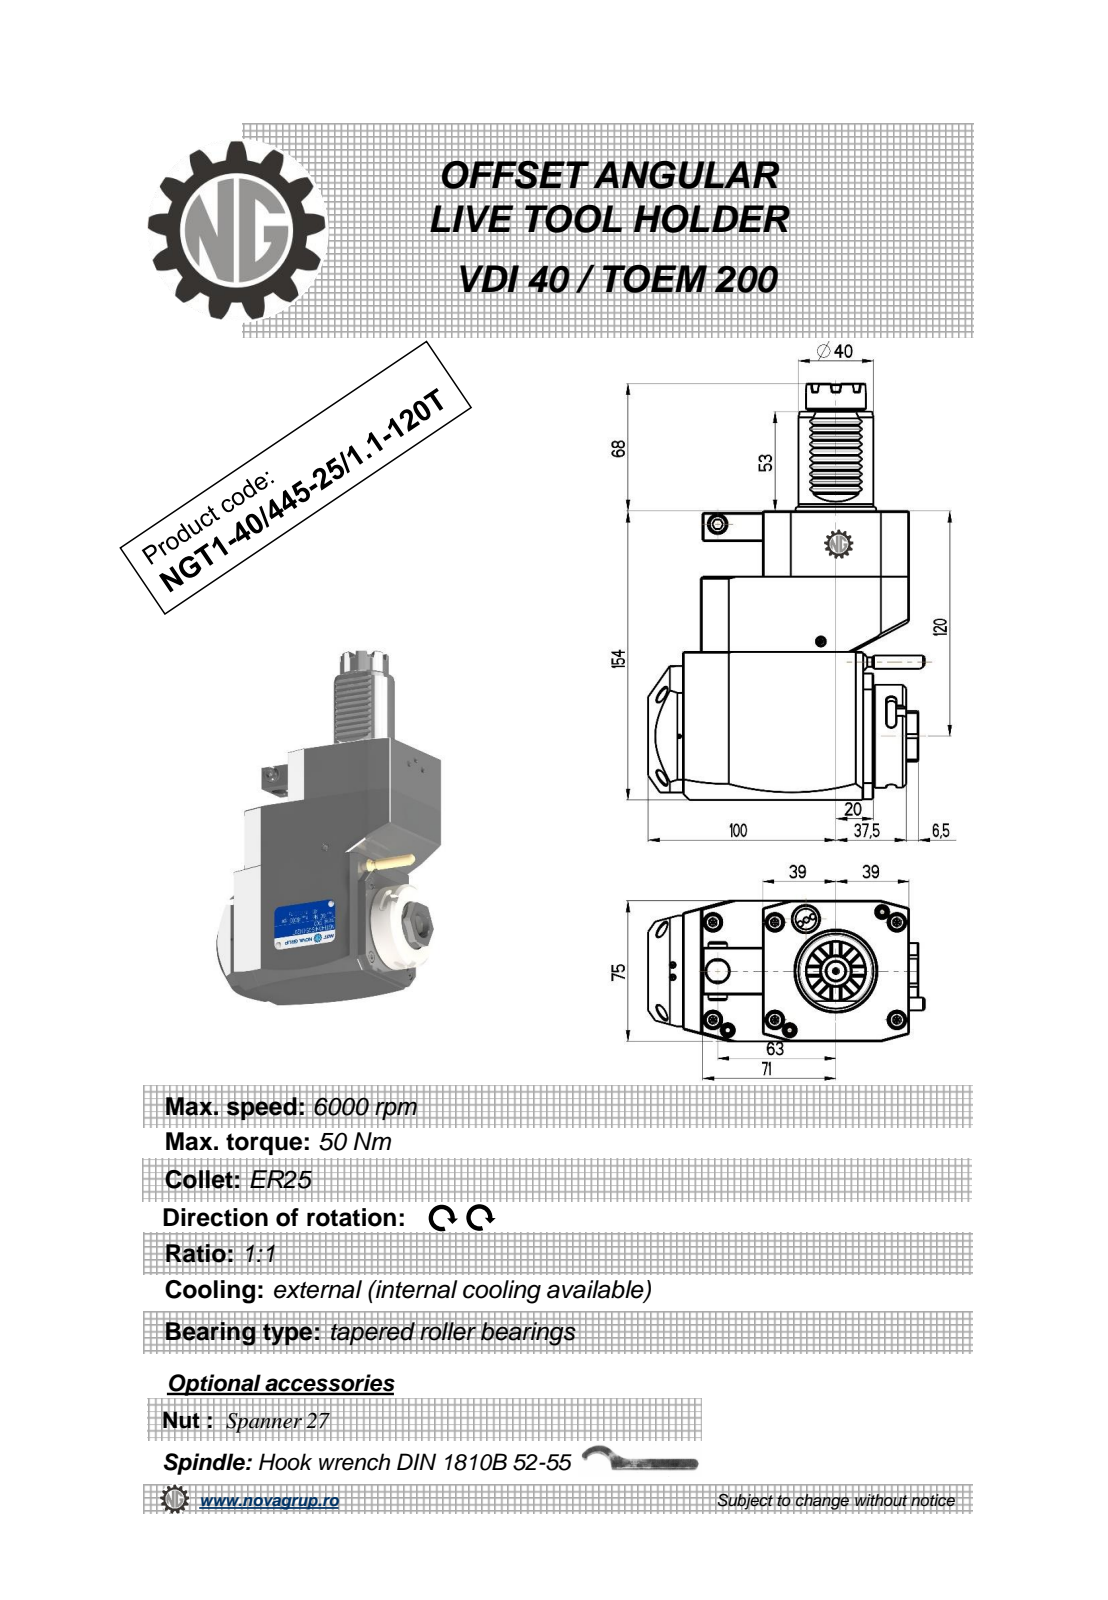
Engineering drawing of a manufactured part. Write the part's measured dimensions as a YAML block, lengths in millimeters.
part_name: "NGT1_40_445_25_1_1_120T"
step_written_by: "PRO/ENGINEER BY PARAMETRIC TECHNOLOGY CORPORATION, 2010280 (CONFIG_CONTROL_DESIGN)"
units: millimeters
bodies: {solids: 1, faces: 411, planar: 225, cylindrical: 78, other: 108}
overall_size: [222, 147.33, 75]
volume: 1266000
surface_area: 89573
round_holes:
  - {diameter: 2.5, count: 1}
  - {diameter: 3, count: 1}
  - {diameter: 8.5, count: 1}
  - {diameter: 9.5, count: 1}
  - {diameter: 12, count: 1}
  - {diameter: 18, count: 1}
round_bosses_or_shafts:
  - {diameter: 8.96, count: 2}
  - {diameter: 55, count: 1}
  - {diameter: 48, count: 1}
  - {diameter: 40, count: 1}
  - {diameter: 32, count: 1}
  - {diameter: 16.8, count: 1}
  - {diameter: 10, count: 1}
  - {diameter: 7, count: 1}
partial_cylinders:
  - {radius: 0.3, count: 10}
  - {radius: 2.5, count: 6}
  - {radius: 180, count: 2}
  - {radius: 0.5, count: 1}
  - {radius: 8.6, count: 1}
  - {radius: 15, count: 1}
  - {radius: 24.5, count: 1}
  - {radius: 37.5, count: 1}
face_to_face_distances: [75, 154, 119, 19, 59, 111, 35, 92, 17.5, 33]
hole_center_spacings: [43.2, 75.07, 112.5]
